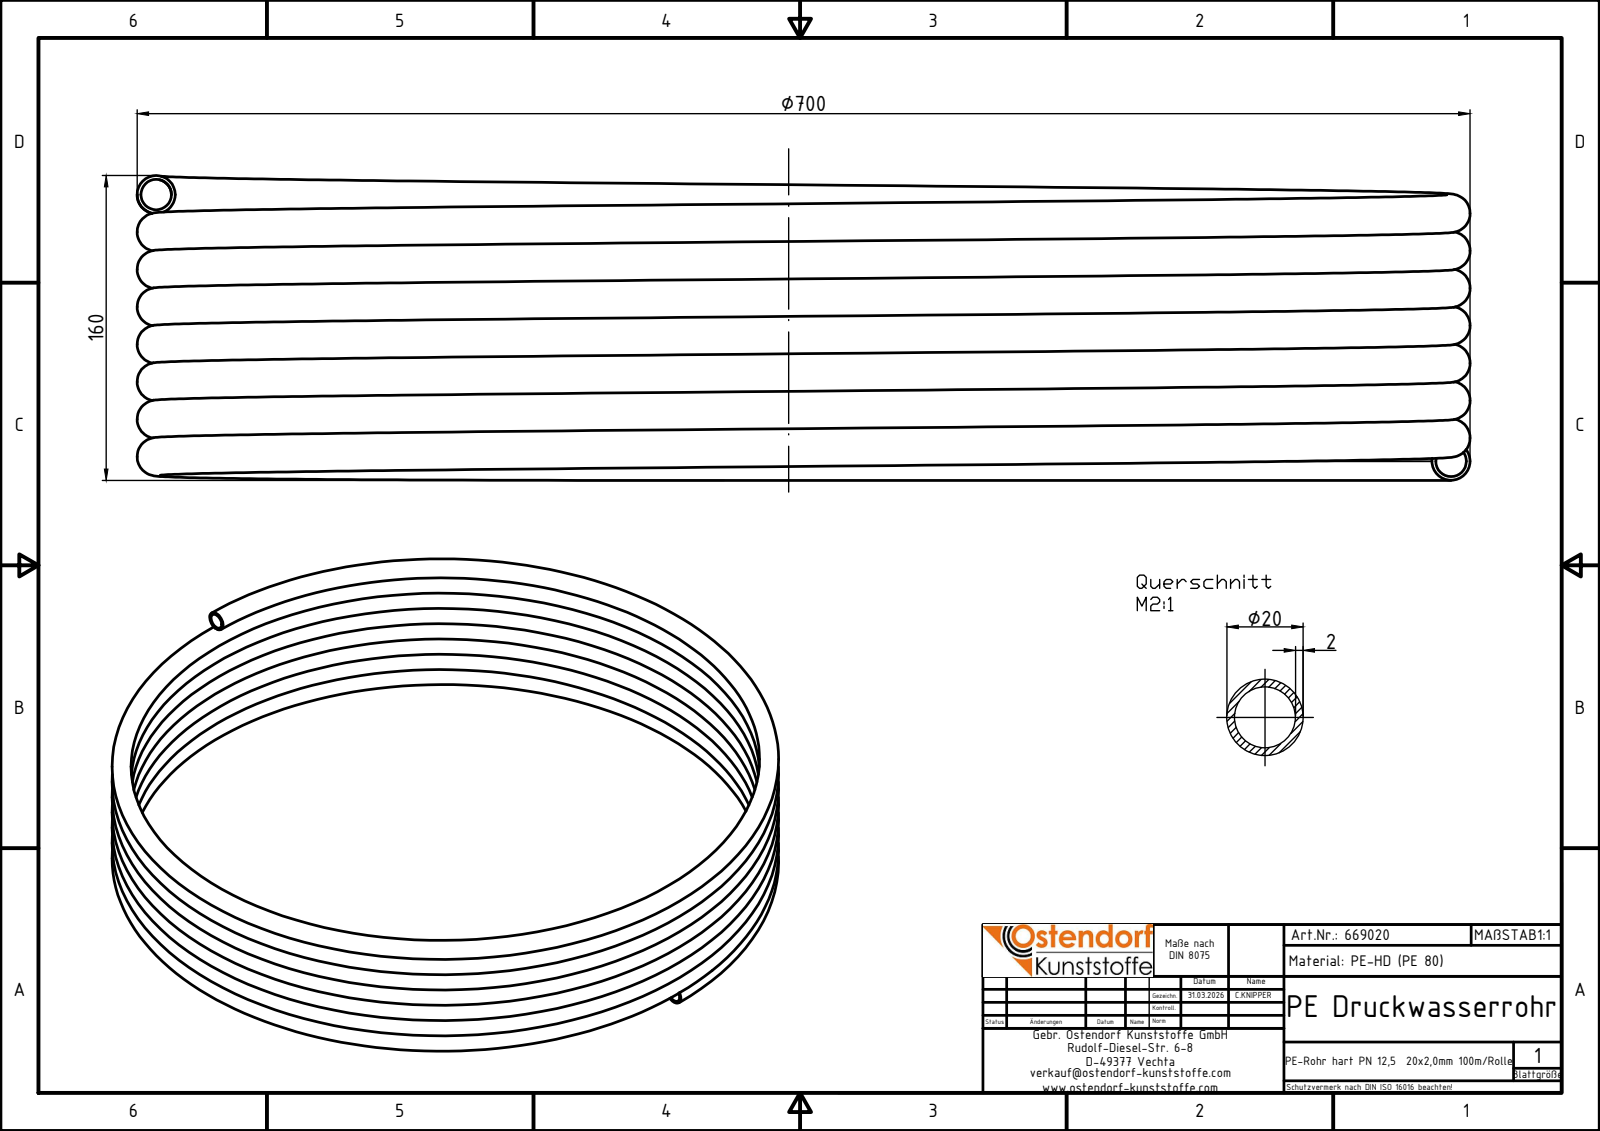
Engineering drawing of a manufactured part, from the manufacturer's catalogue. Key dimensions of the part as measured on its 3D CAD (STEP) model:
Part name (STEP PRODUCT): 669020z
STEP written by: Autodesk Inventor 2024 (AUTOMOTIVE_DESIGN)
Units: millimetres
Bodies: 1 solid, 7 faces (3 planar, 0 cylindrical, 4 other)
Overall size (bounding box): 700.01 × 700 × 160.08
Volume: 1 778 000 mm³ · Surface area: 1 689 000 mm²
